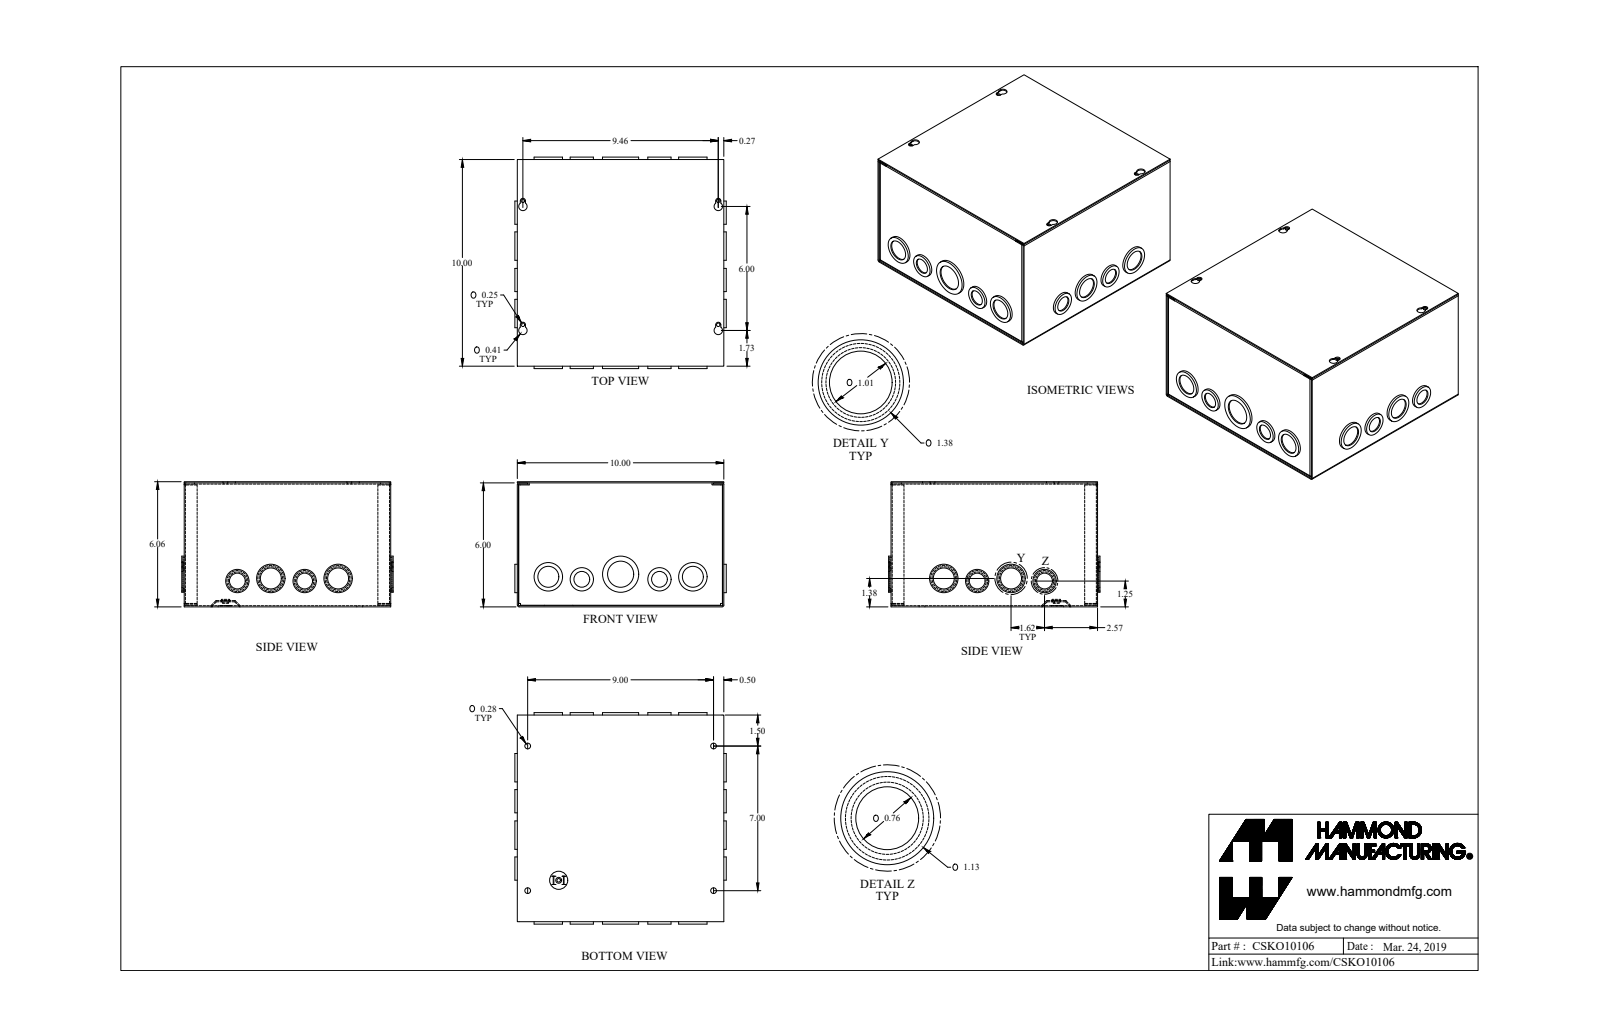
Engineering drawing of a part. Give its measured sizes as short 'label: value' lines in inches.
name: CSKO10106_Default
written by: SolidWorks 2019 (CONFIG_CONTROL_DESIGN)
unit: in
bodies: 4 solids, 421 faces (197 planar, 216 cylindrical, 8 other)
size: 10.234 × 10.234 × 6.057
volume: 27.62 in³; area: 980.2 in²
holes: 8× ⌀1.011, 6× ⌀1.261, 5× ⌀0.17, 4× ⌀0.281, 4× ⌀0.761, 1× ⌀0.5, 1× ⌀1.636
bosses: 5× ⌀1.375, 5× ⌀1.125, 4× ⌀0.875, 3× ⌀1.375, 3× ⌀1.125, 2× ⌀0.875, 1× ⌀1.75, 1× ⌀0.492
rounds: 12× R0.029, 12× R0.086, 8× R0.057, 4× R0.125, 4× R0.203
face distances: 0.057, 9.943, 6, 10, 5.943, 9.886, 6.057, 0.114, 0.07, 9.873
hole spacings: 1.625, 0.55, 6.504, 9.243, 11.289, 3.26, 7, 1.896
